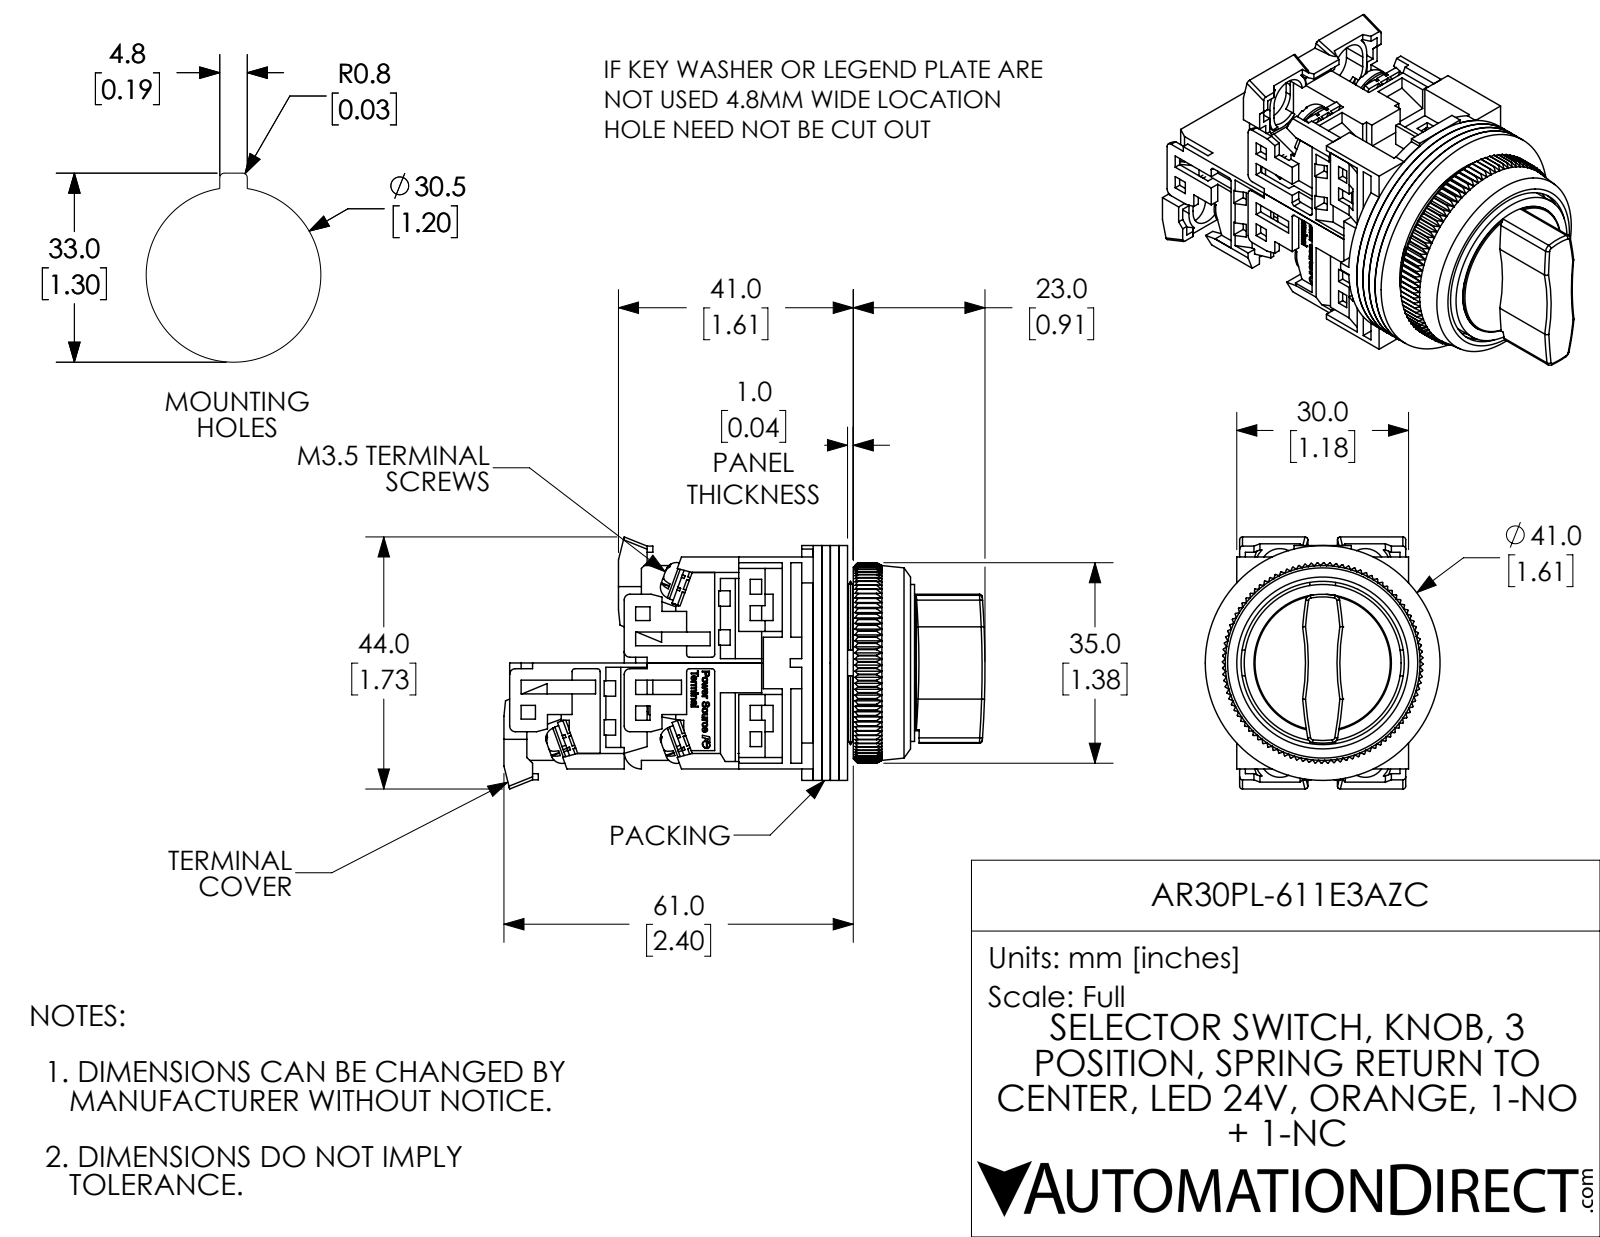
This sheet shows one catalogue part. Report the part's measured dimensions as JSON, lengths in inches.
{"part_name": "AR30PL-611E3AZC", "step_written_by": "SolidWorks 2017 (AUTOMOTIVE_DESIGN)", "units": "inches", "bodies": {"solids": 32, "faces": 2783, "planar": 2039, "cylindrical": 338, "other": 406}, "overall_size": [3.307, 1.732, 1.614], "volume_in3": 2.677, "surface_area_in2": 66.54, "round_holes": [[0.138, 10], [0.142, 6], [0.118, 1], [0.472, 1], [0.709, 1], [0.768, 1], [0.827, 1], [1.122, 1], [1.181, 1], [1.252, 1]], "round_bosses_or_shafts": [[0.26, 6], [0.138, 6], [0.063, 2], [1.614, 1], [1.15, 1], [1.079, 1], [0.945, 1], [0.886, 1]], "partial_cylinders_radius": [[0.059, 24], [0.02, 14], [0.039, 10], [0.138, 4], [0.177, 4], [0.118, 3], [1.575, 2], [2.953, 2]], "face_to_face_distances": [0.059, 0.118, 0.177, 0.039, 0.787, 0.063, 0.079, 0.02, 0.811, 0.689], "hole_center_spacings": [0.579, 0.269, 0.638, 0.61]}
